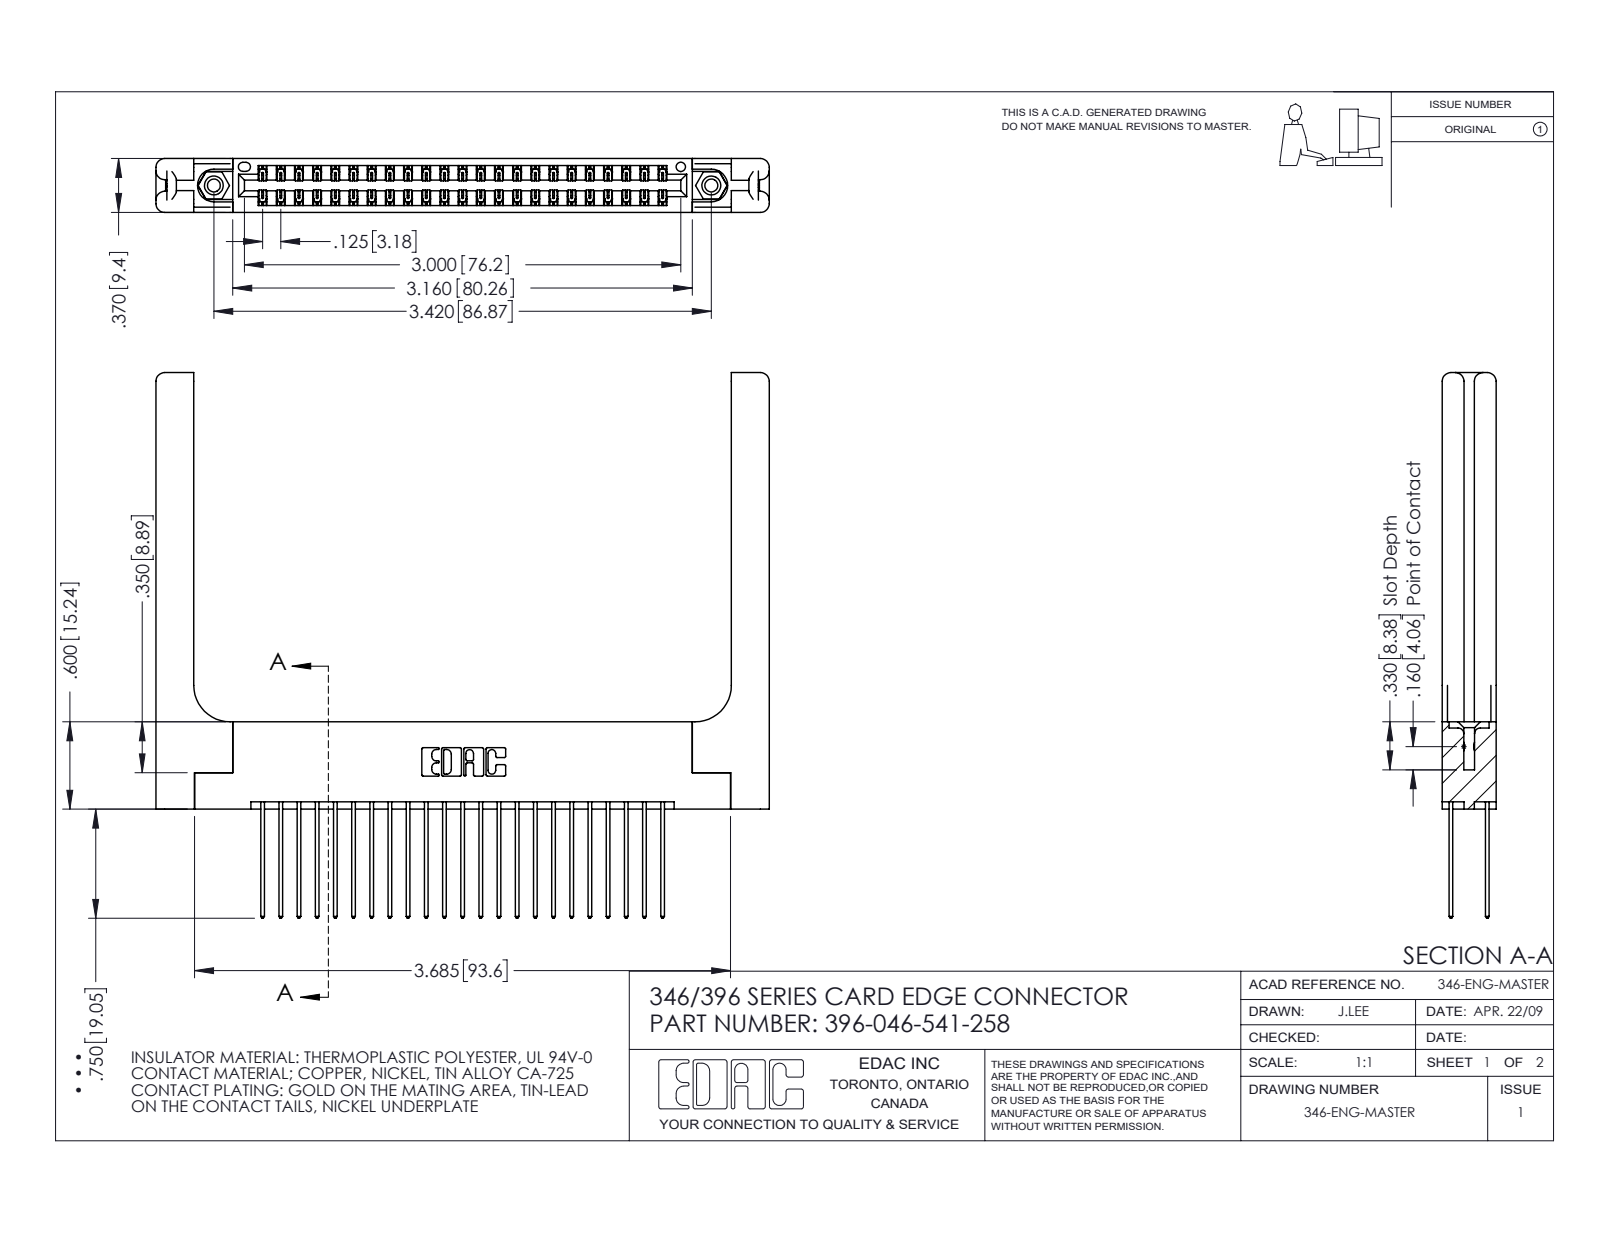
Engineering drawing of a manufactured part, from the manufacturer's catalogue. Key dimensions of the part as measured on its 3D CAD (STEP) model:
Part name (STEP PRODUCT): 345-250-001_345-250-001-102; 346 Part_Flush Mounting Lugs - 0.156 Dia-TH; 345-292-001_345-293-141; 346-220-058_345-220-058 (+1 more)
STEP written by: SolidWorks 2016 (CONFIG_CONTROL_DESIGN)
Units: inches
Bodies: 51 solids, 2770 faces (1834 planar, 876 cylindrical, 60 other)
Overall size (bounding box): 4.216 × 3.75 × 0.37
Volume: 1.102 in³ · Surface area: 31.7 in²
Round holes (diameter × count): ⌀0.089 ×2, ⌀0.125 ×2, ⌀0.156 ×2, ⌀0.064 ×1
Round bosses / shafts (diameter × count): ⌀0.155 ×2
Partial cylindrical surfaces — rounded edges, fillets, slot ends (radius × count): R0.006 ×69, R0.01 ×46, R0.01 ×22, R0.06 ×16, R0.007 ×6, R0.031 ×6, R0.026 ×3, R0.014 ×2
Main face-to-face distances: 0.072, 0.37, 0.048, 0.322, 0.25, 0.025, 0.298, 0.148, 0.15, 0.275
Hole centre spacings: 0.246, 3.212, 3.42
